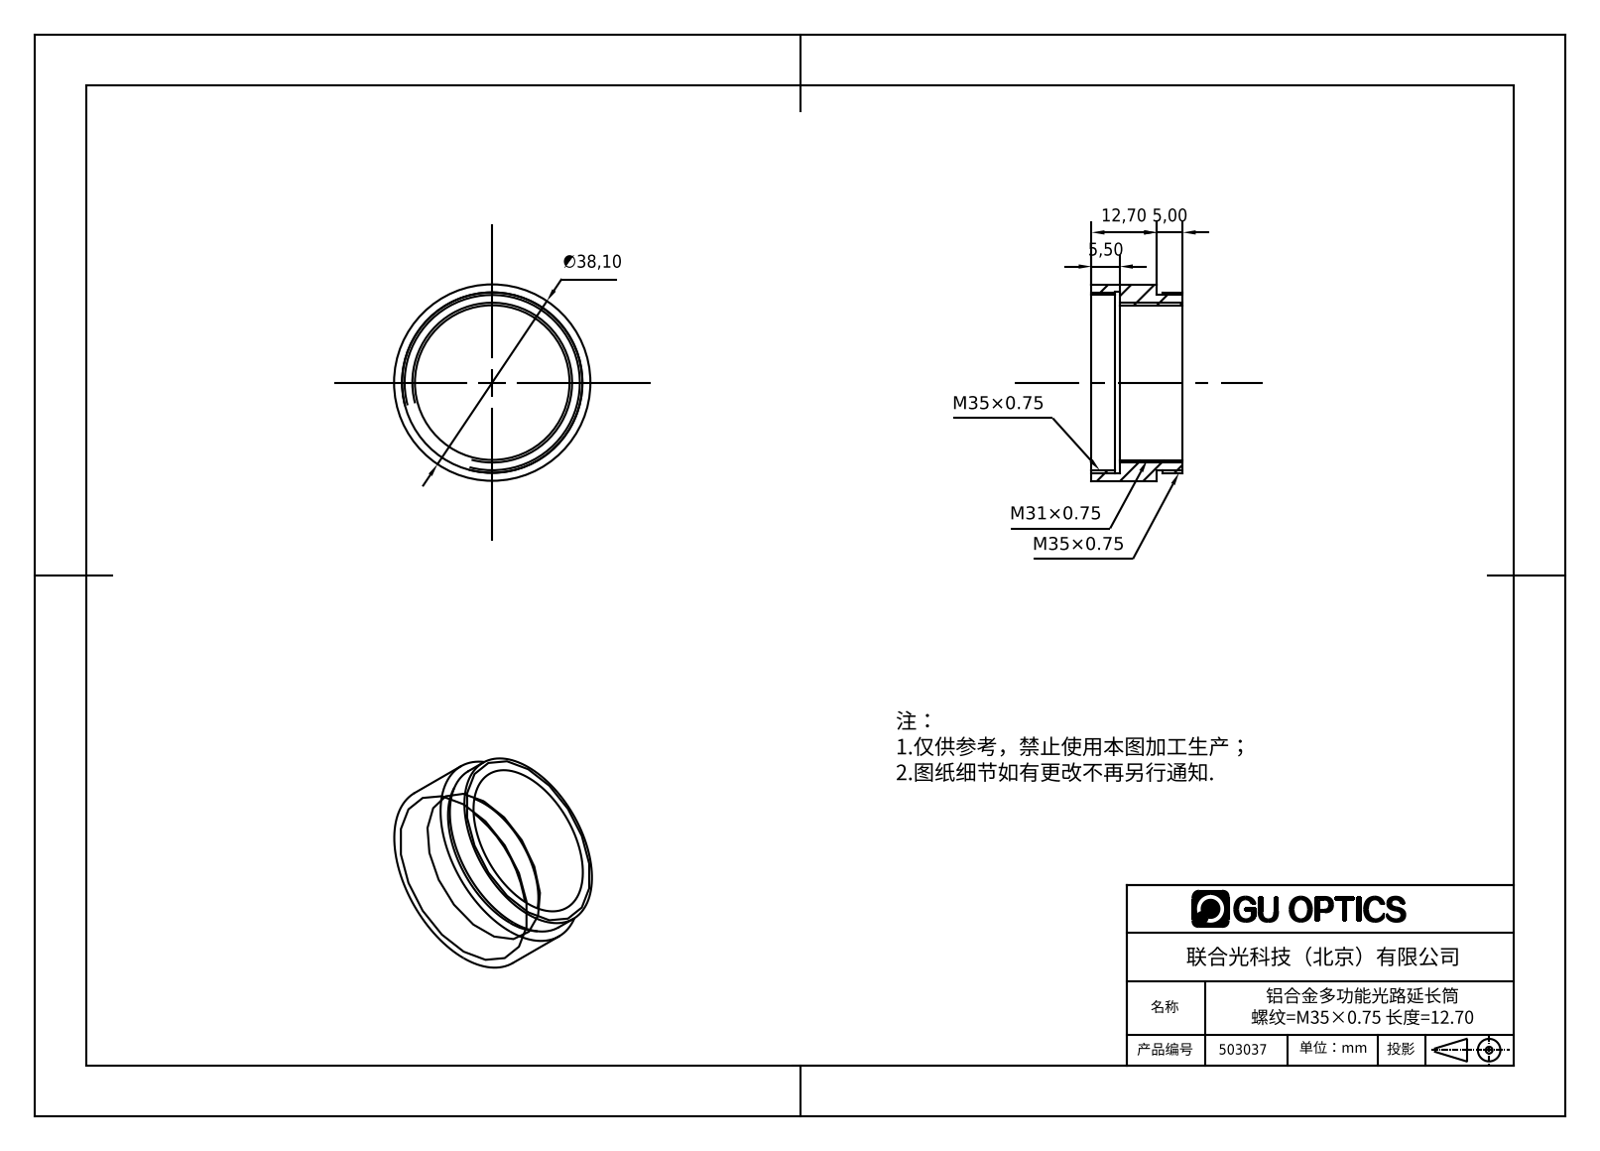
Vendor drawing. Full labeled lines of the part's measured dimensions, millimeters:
Part name (STEP PRODUCT): 503037
STEP written by: SolidWorks 2016 (AUTOMOTIVE_DESIGN)
Units: millimetres
Bodies: 1 solid, 18 faces (6 planar, 12 cylindrical, 0 other)
Overall size (bounding box): 38.1 × 38.1 × 17.7
Volume: 5 553 mm³ · Surface area: 4 913 mm²
Round holes (diameter × count): ⌀30 ×1, ⌀34 ×1, ⌀35.2 ×1
Round bosses / shafts (diameter × count): ⌀38.1 ×1, ⌀35 ×1
Main face-to-face distances: 12.2, 7.2, 5, 5.5, 12.7, 17.7, 1, 8.2, 4.5, 13.2
